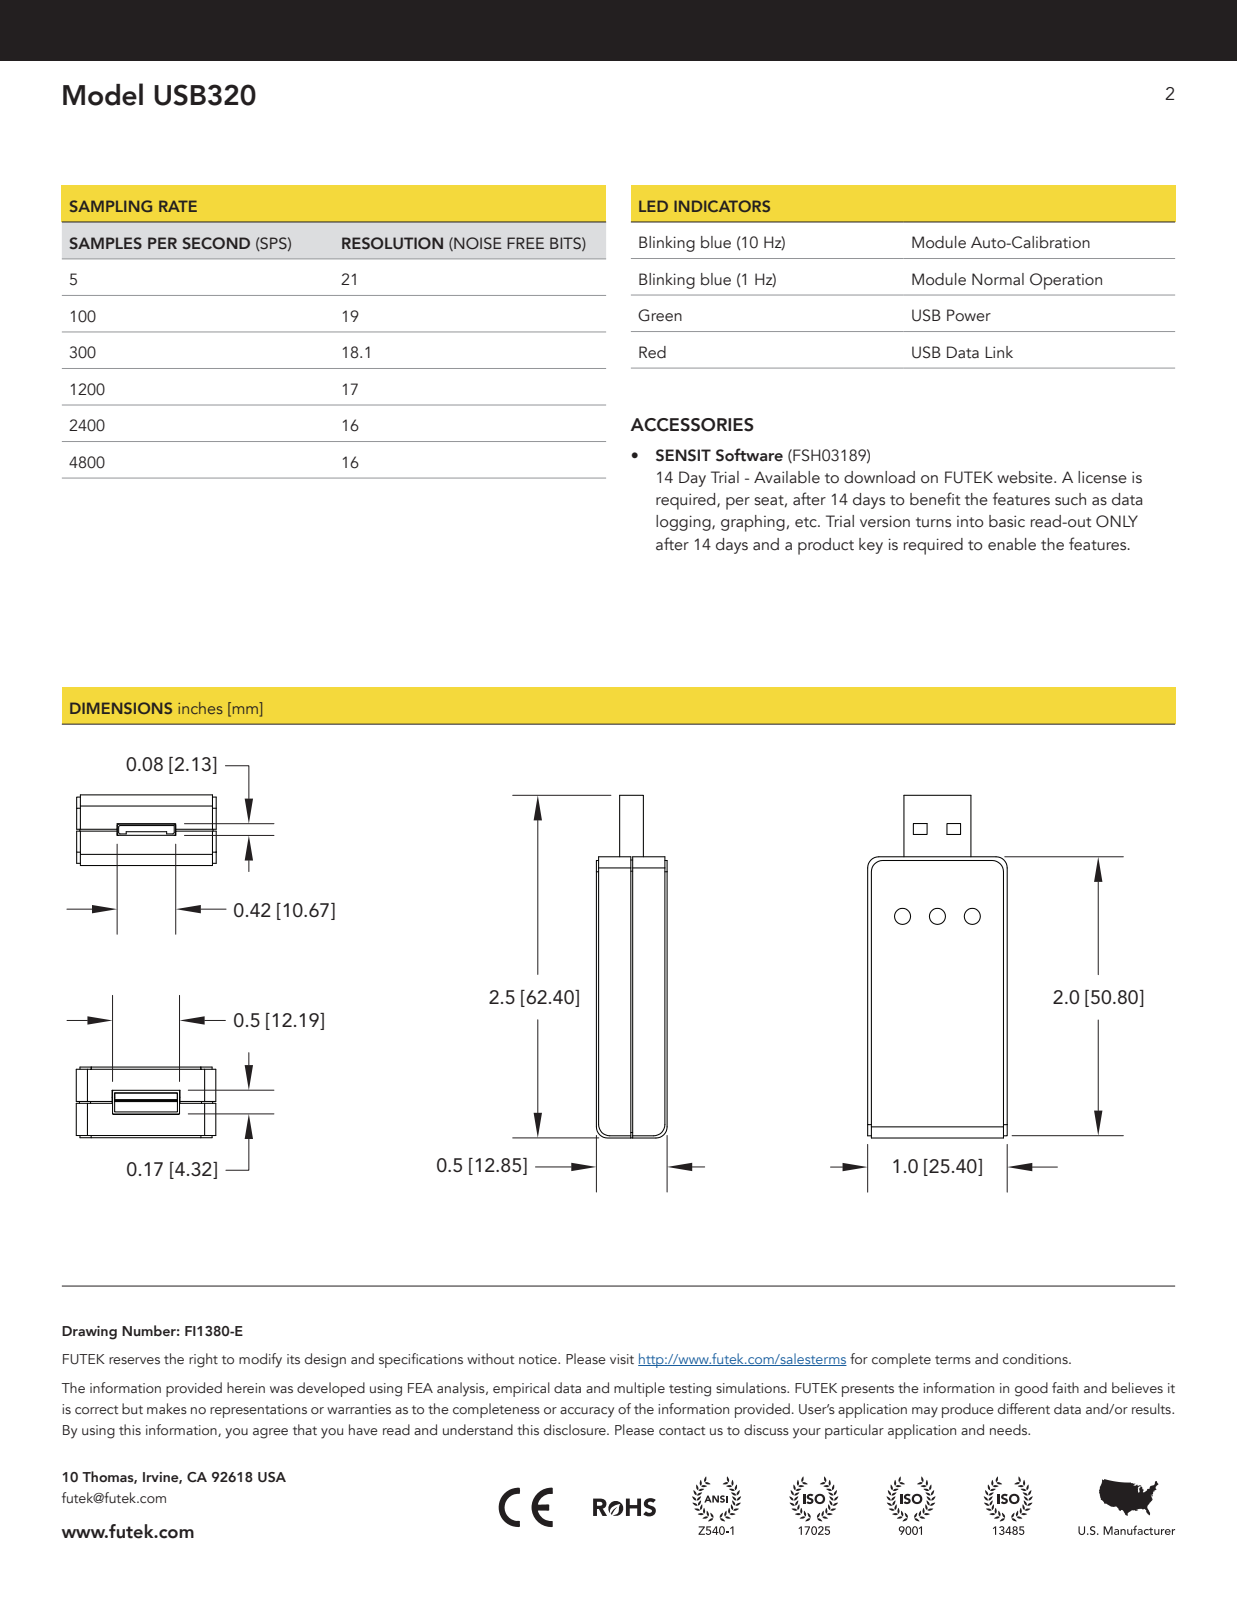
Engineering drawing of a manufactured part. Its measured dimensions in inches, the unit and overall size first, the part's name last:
Units: inches
Overall size (bounding box): 2.503 × 0.998 × 0.5
Round holes (diameter × count): ⌀0.104 ×3
Partial cylindrical surfaces — rounded edges, fillets, slot ends (radius × count): R0.006 ×8, R0.01 ×8, R0.012 ×8, R0.004 ×4, R0.009 ×4, R0.011 ×4, R0.015 ×4, R0.016 ×4
Main face-to-face distances: 0.5, 0.996, 0.173, 0.327, 0.161, 0.339, 0.165, 0.174, 0.326, 0.153
Hole centre spacings: 0.25, 0.5
Volume: 0.978 in³ · Surface area: 9.261 in²
Bodies: 1 solid, 292 faces (211 planar, 53 cylindrical, 28 other)
Part name (STEP PRODUCT): USB320_Shrinkwrap_1
STEP written by: Autodesk Inventor 2018 (AUTOMOTIVE_DESIGN)
